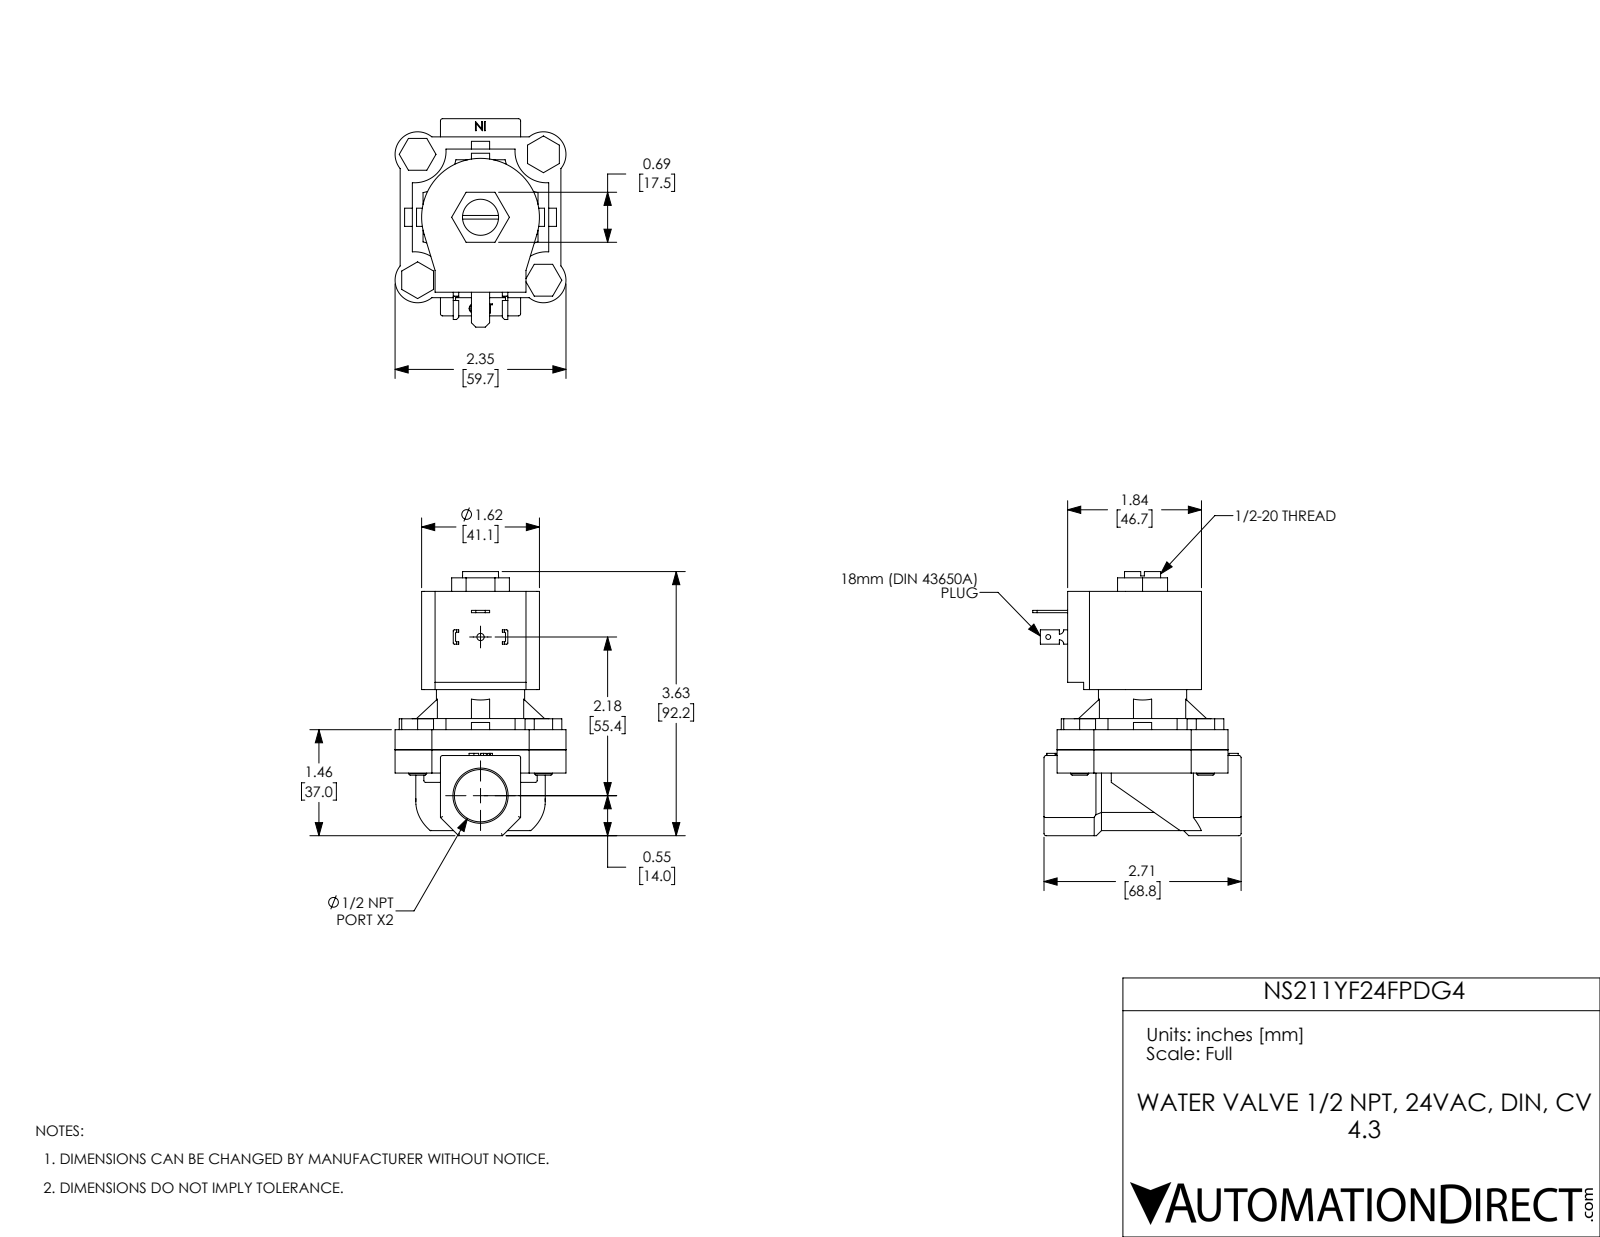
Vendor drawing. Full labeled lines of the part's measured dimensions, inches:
Part name (STEP PRODUCT): NS211YF24FPDG4
STEP written by: SolidWorks 2017 (AUTOMOTIVE_DESIGN)
Units: inches
Bodies: 11 solids, 385 faces (239 planar, 113 cylindrical, 33 other)
Overall size (bounding box): 3.63 × 2.865 × 2.35
Volume: 9.473 in³ · Surface area: 65.14 in²
Round holes (diameter × count): ⌀0.25 ×4, ⌀0.067 ×1, ⌀0.1 ×1, ⌀0.496 ×1, ⌀0.512 ×1, ⌀0.719 ×1, ⌀1.155 ×1
Round bosses / shafts (diameter × count): ⌀0.248 ×4, ⌀1.213 ×1
Partial cylindrical surfaces — rounded edges, fillets, slot ends (radius × count): R0.03 ×15, R0.015 ×8, R0.31 ×4, R0.432 ×4, R0.579 ×4, R0.06 ×2, R0.81 ×1, R0.89 ×1
Main face-to-face distances: 0.276, 2.177, 1.901, 0.32, 0.596, 2.497, 0.554, 1.656, 0.25, 1.147
Hole centre spacings: 1.223, 1.73, 2.446, 2.181
